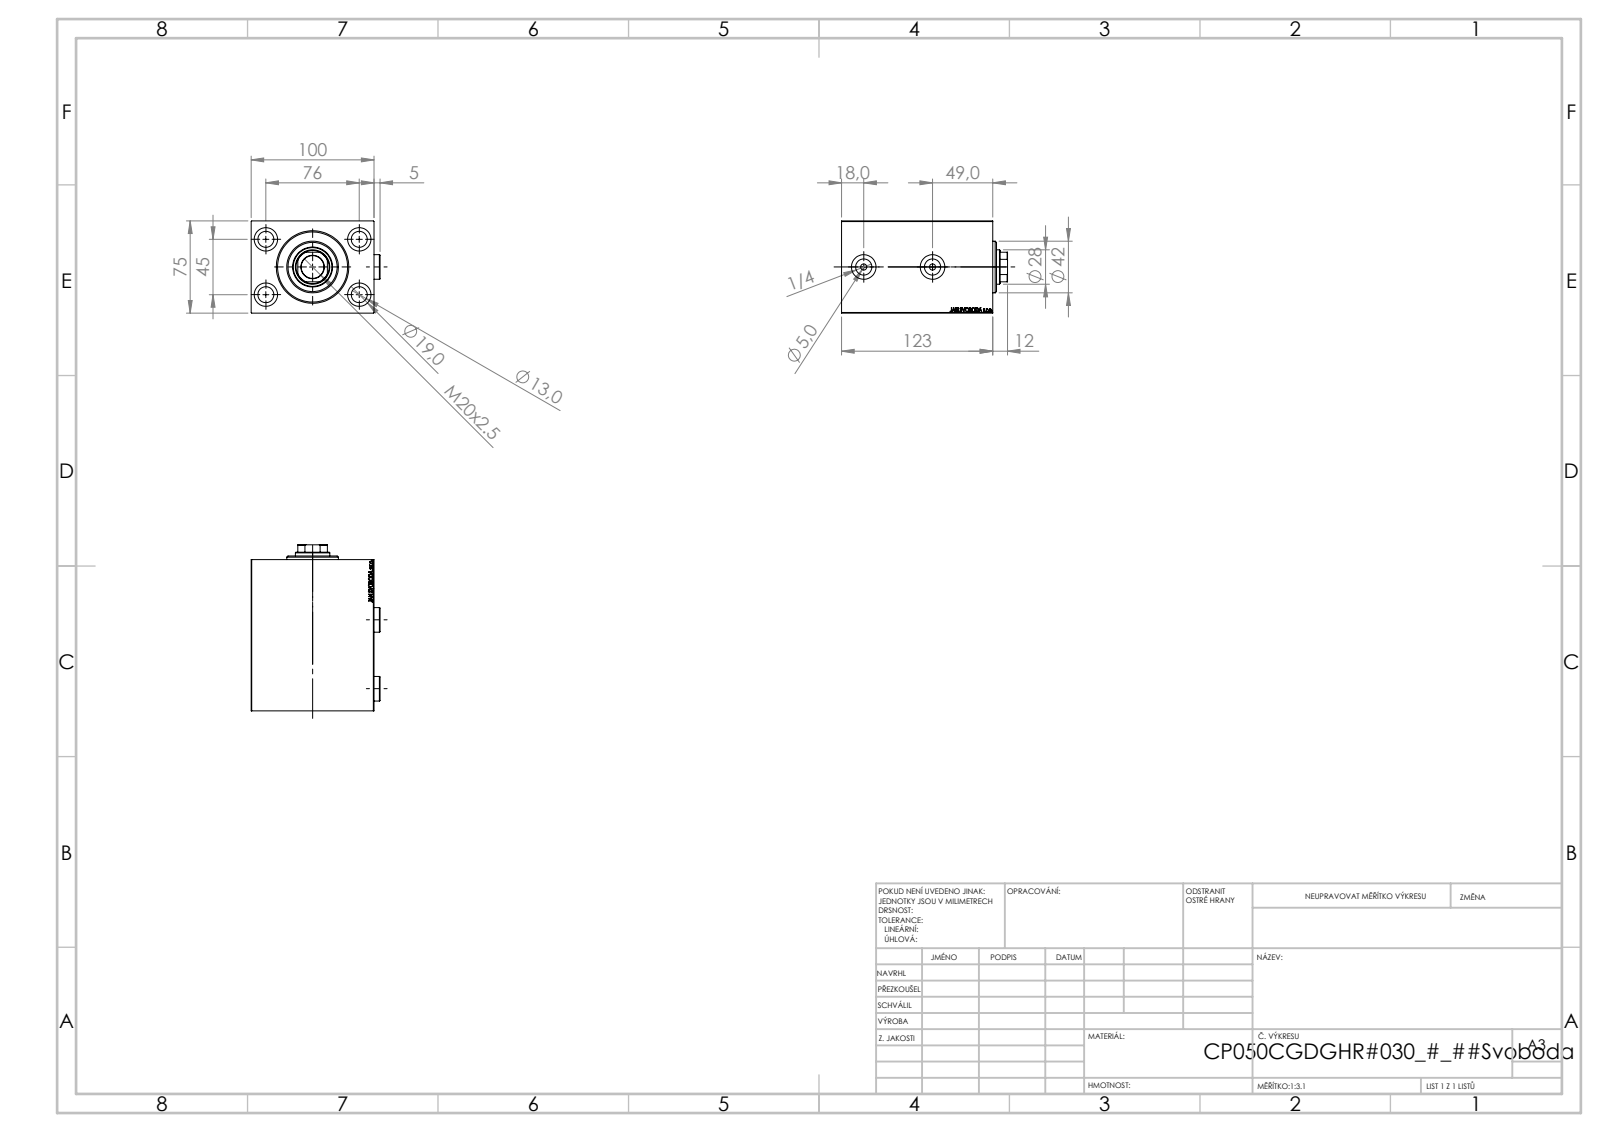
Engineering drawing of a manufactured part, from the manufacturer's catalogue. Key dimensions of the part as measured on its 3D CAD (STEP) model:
Part name (STEP PRODUCT): PLUG; V450CP_C; V450CP_VC_B; V450CP_B_VCP
STEP written by: SolidWorks 2019 (CONFIG_CONTROL_DESIGN)
Units: millimetres
Bodies: 5 solids, 943 faces (449 planar, 92 cylindrical, 402 other)
Overall size (bounding box): 135 × 104.9 × 75
Volume: 795 766 mm³ · Surface area: 136 684 mm²
Round holes (diameter × count): ⌀13 ×4, ⌀19 ×4, ⌀4 ×2, ⌀5 ×2, ⌀9.73 ×2, ⌀13.16 ×2, ⌀15 ×2, ⌀20 ×2, ⌀18.5 ×1, ⌀28 ×1, ⌀31.5 ×1, ⌀32.5 ×1
Round bosses / shafts (diameter × count): ⌀42 ×1
Partial cylindrical surfaces — rounded edges, fillets, slot ends (radius × count): R13.5 ×1
Main face-to-face distances: 75, 100, 123, 14, 109, 30, 74, 44, 49, 60
Hole centre spacings: 44.16, 45, 76, 88.32, 42.55, 56
